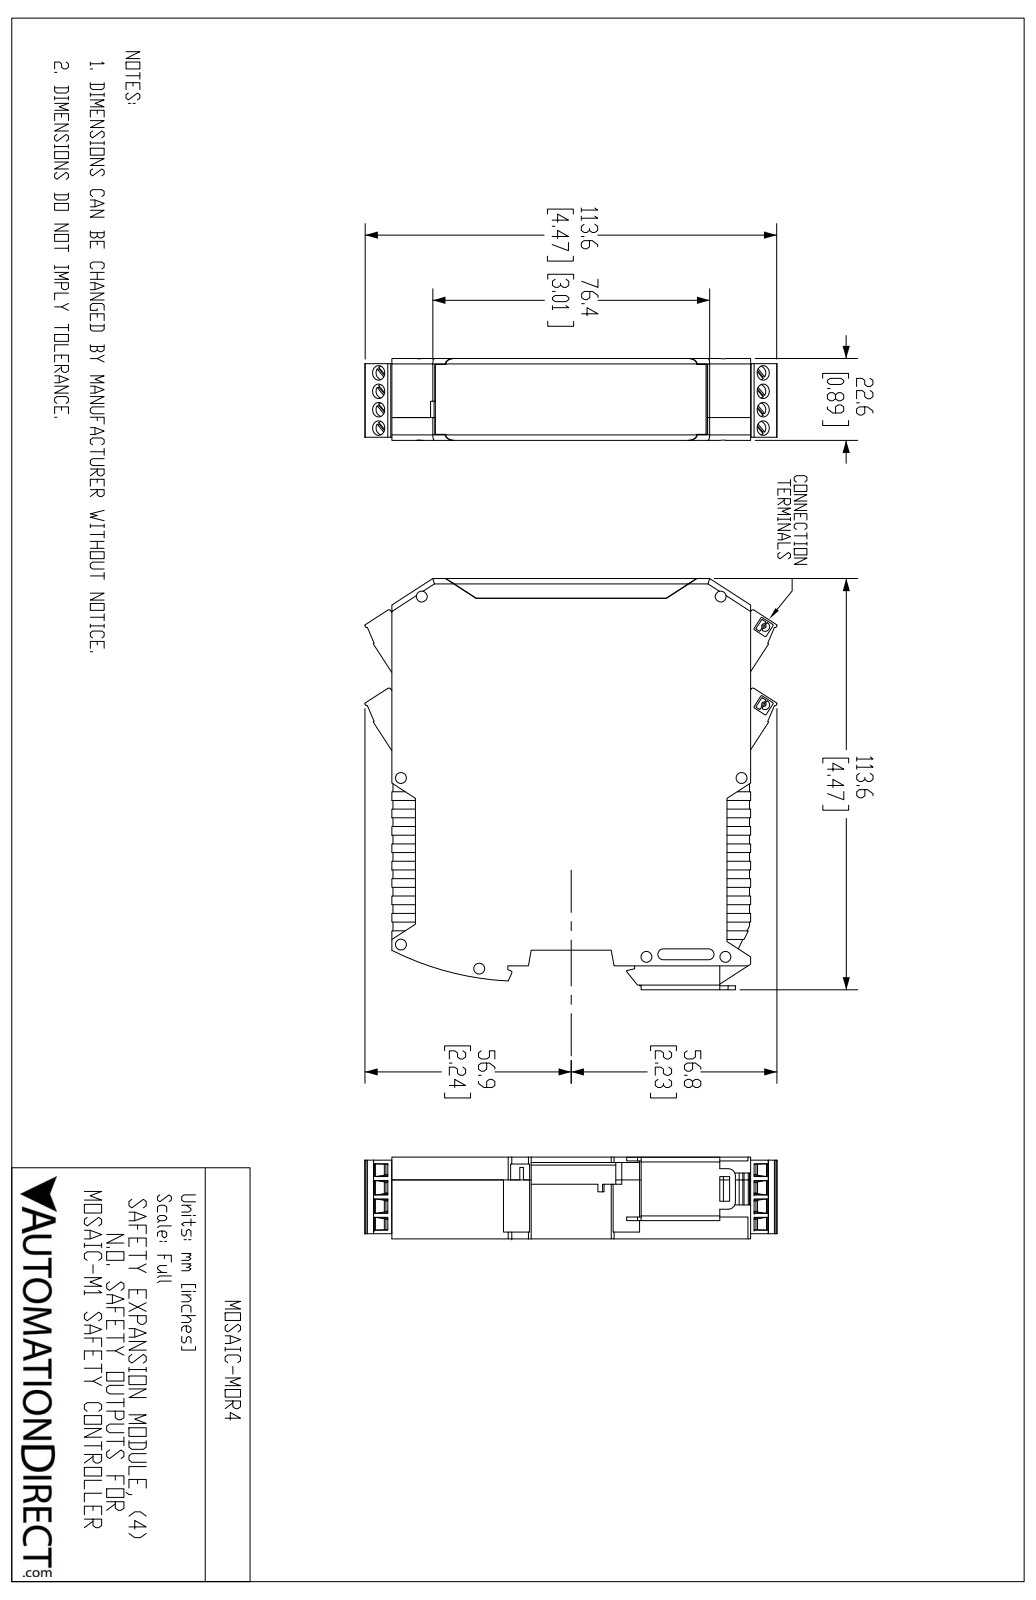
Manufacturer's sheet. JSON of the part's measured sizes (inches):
{"part_name": "MOSAIC-MOR4", "step_written_by": "SolidWorks 2017 (AUTOMOTIVE_DESIGN)", "units": "inches", "bodies": {"solids": 11, "faces": 1831, "planar": 1497, "cylindrical": 299, "other": 35}, "overall_size": [4.478, 4.472, 0.89], "volume_in3": 3.914, "surface_area_in2": 126.1, "round_holes": [[0.157, 16], [0.118, 14], [0.11, 12], [0.055, 10], [0.063, 1]], "round_bosses_or_shafts": [[0.149, 16], [0.024, 4], [0.177, 1], [0.11, 1], [0.053, 1]], "partial_cylinders_radius": [[0.008, 40], [0.008, 16], [0.011, 16], [0.028, 16], [0.115, 16], [0.012, 13], [0.03, 12], [0.059, 8]], "face_to_face_distances": [0.049, 0.841, 0.89, 0.791, 0.039, 2.67, 0.062, 2.67, 2.732, 2.608], "hole_center_spacings": [0.2, 0.4, 0.505, 0.741, 0.463, 0.612, 0.713, 0.2]}
